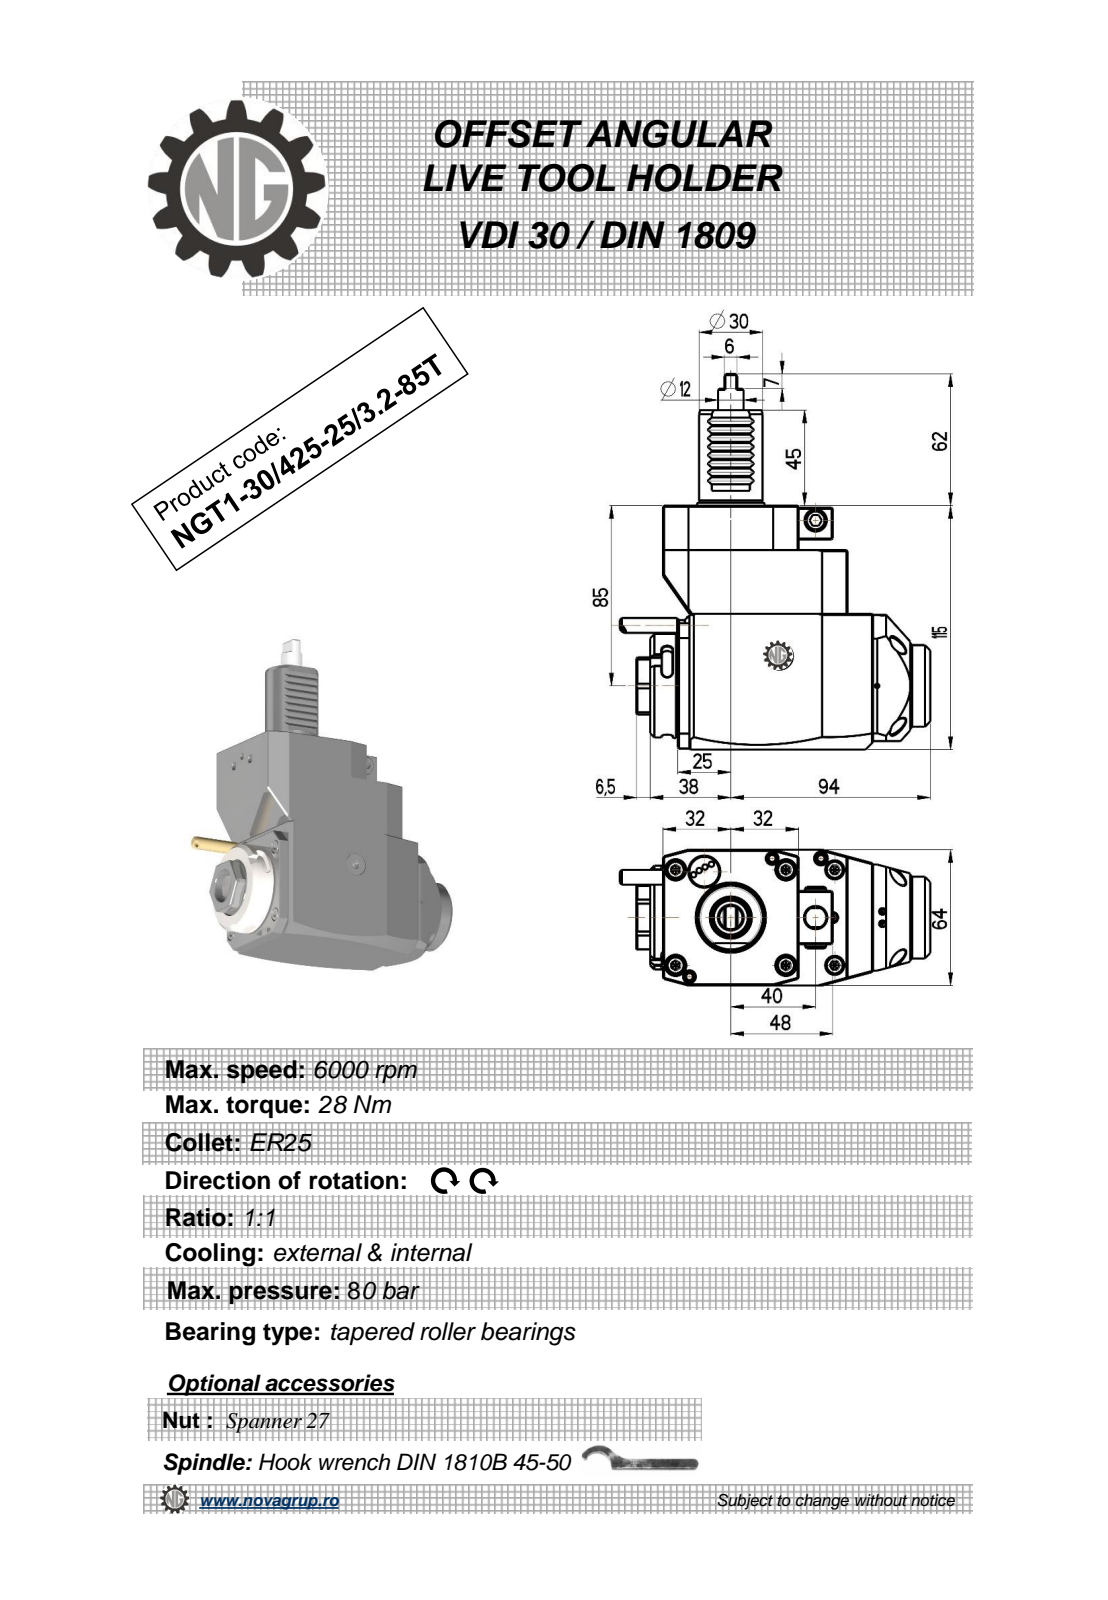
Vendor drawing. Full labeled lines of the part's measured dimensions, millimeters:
Part name (STEP PRODUCT): NGT1_30_425_25_3_2_85T
STEP written by: PRO/ENGINEER BY PARAMETRIC TECHNOLOGY CORPORATION, 2010280 (CONFIG_CONTROL_DESIGN)
Units: millimetres
Bodies: 1 solid, 331 faces (189 planar, 70 cylindrical, 72 other)
Overall size (bounding box): 177 × 146.38 × 64
Volume: 716 749 mm³ · Surface area: 59 494 mm²
Round holes (diameter × count): ⌀2.5 ×1, ⌀3 ×1, ⌀8.5 ×1, ⌀9.5 ×1, ⌀10 ×1, ⌀18 ×1
Round bosses / shafts (diameter × count): ⌀8.96 ×2, ⌀49 ×1, ⌀42 ×1, ⌀38.5 ×1, ⌀30 ×1, ⌀12 ×1, ⌀10 ×1, ⌀7 ×1
Partial cylindrical surfaces — rounded edges, fillets, slot ends (radius × count): R0.3 ×8, R2.5 ×6, R0.8 ×2, R180 ×2, R4.5 ×1, R15 ×1, R21.5 ×1, R33.5 ×1
Main face-to-face distances: 64, 115, 7, 80, 87, 6, 94, 21, 12.5, 13
Hole centre spacings: 34.25, 51.62, 76.5
